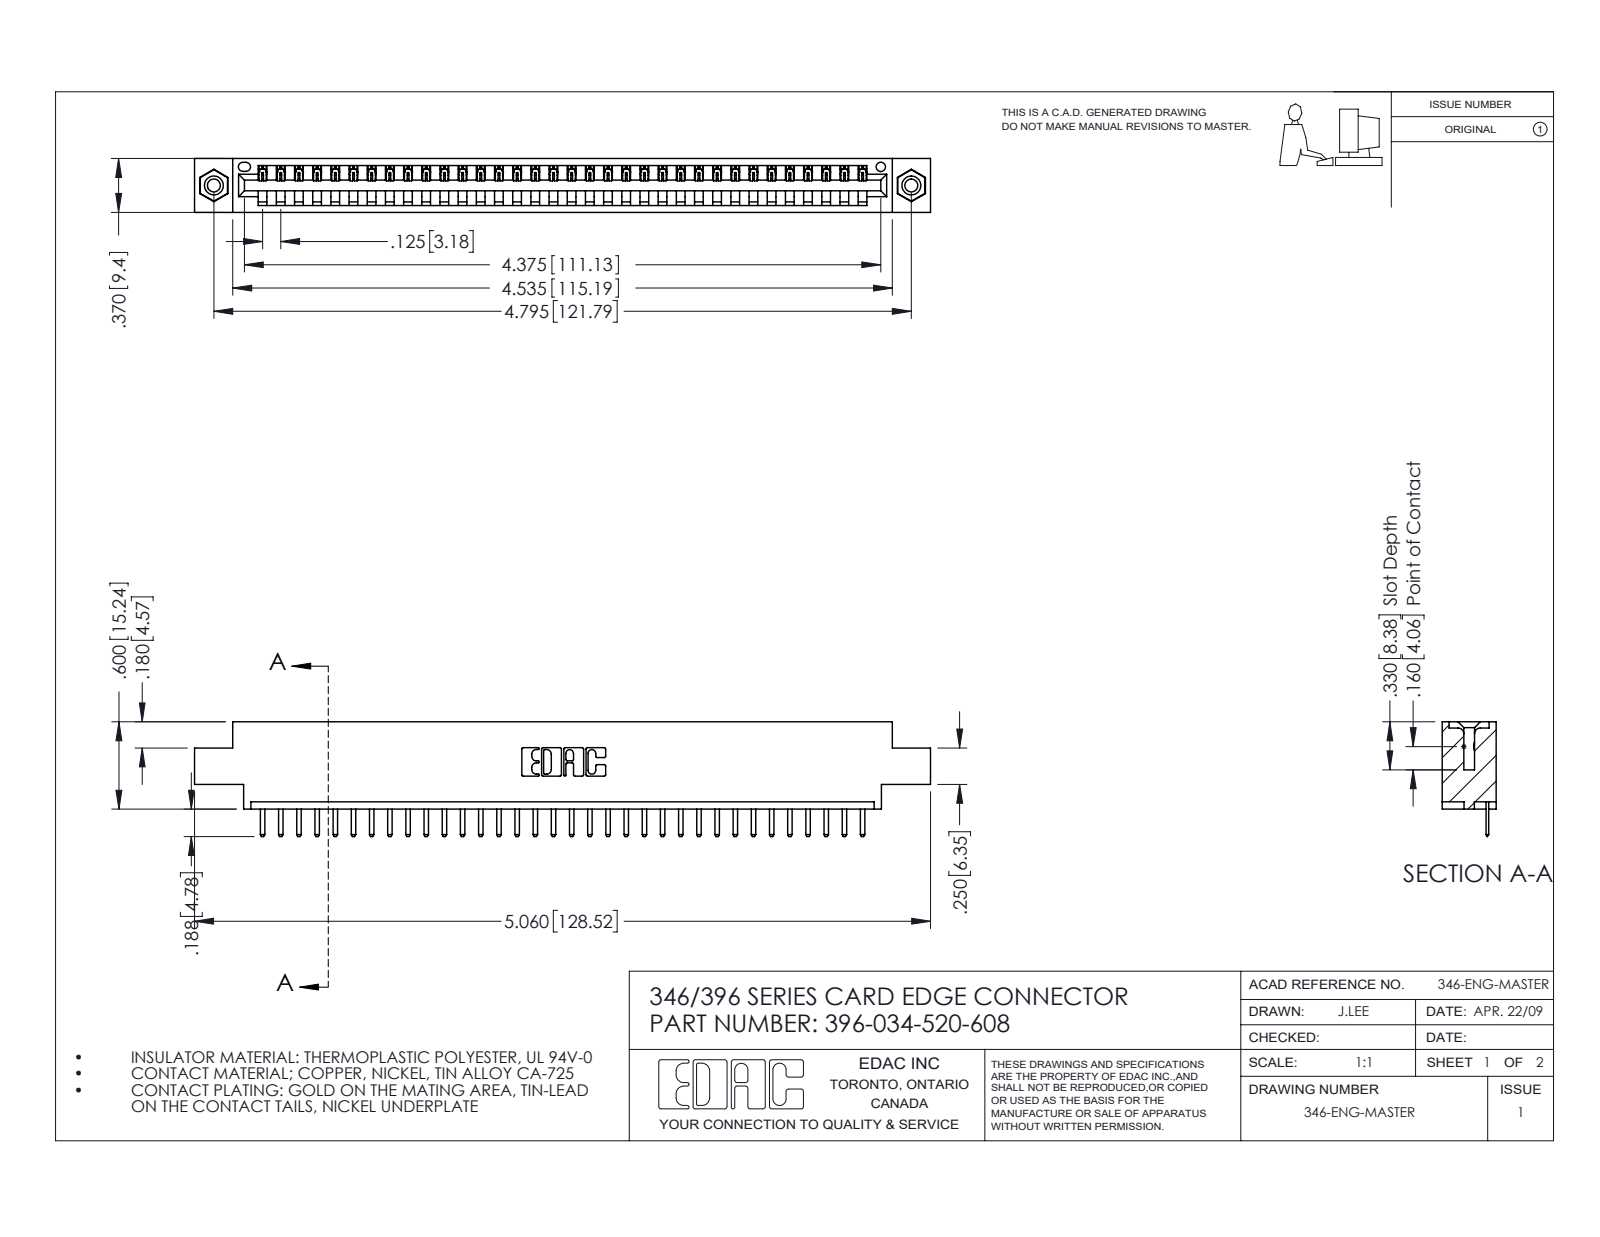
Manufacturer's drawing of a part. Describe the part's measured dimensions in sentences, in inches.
The part is named "346 Part_0.170 Offset - 0.156 Dia-TI; 345-292-001_345-293-120; 396-034-520-608; 345-250-001_345-250-003-102". Its 3-D file was written by "SolidWorks 2016 (CONFIG_CONTROL_DESIGN)". It is 37 solids with 2294 faces: 1540 planar, 738 cylindrical and 16 other. Overall it measures 5.06 by 0.788 by 0.37 inches. Its volume is 0.732 cubic inches and its surface area 22.87 square inches. Round holes: 2 of diameter 0.089, 2 of diameter 0.125, 2 of diameter 0.156, 1 of diameter 0.064. Round bosses or shafts: 2 of diameter 0.155. Partial cylindrical surfaces (rounded edges, fillets, slot ends): 70 of radius 0.01, 68 of radius 0.006, 22 of radius 0.01, 6 of radius 0.007, 6 of radius 0.031, 3 of radius 0.026, 2 of radius 0.031, 2 of radius 0.04. The main face-to-face distances are 0.048, 0.322, 0.37, 0.25, 0.222, 0.148, 0.1, 0.174, 0.072, 0.298. The hole center spacings are 0.246, 4.587, 4.795.
